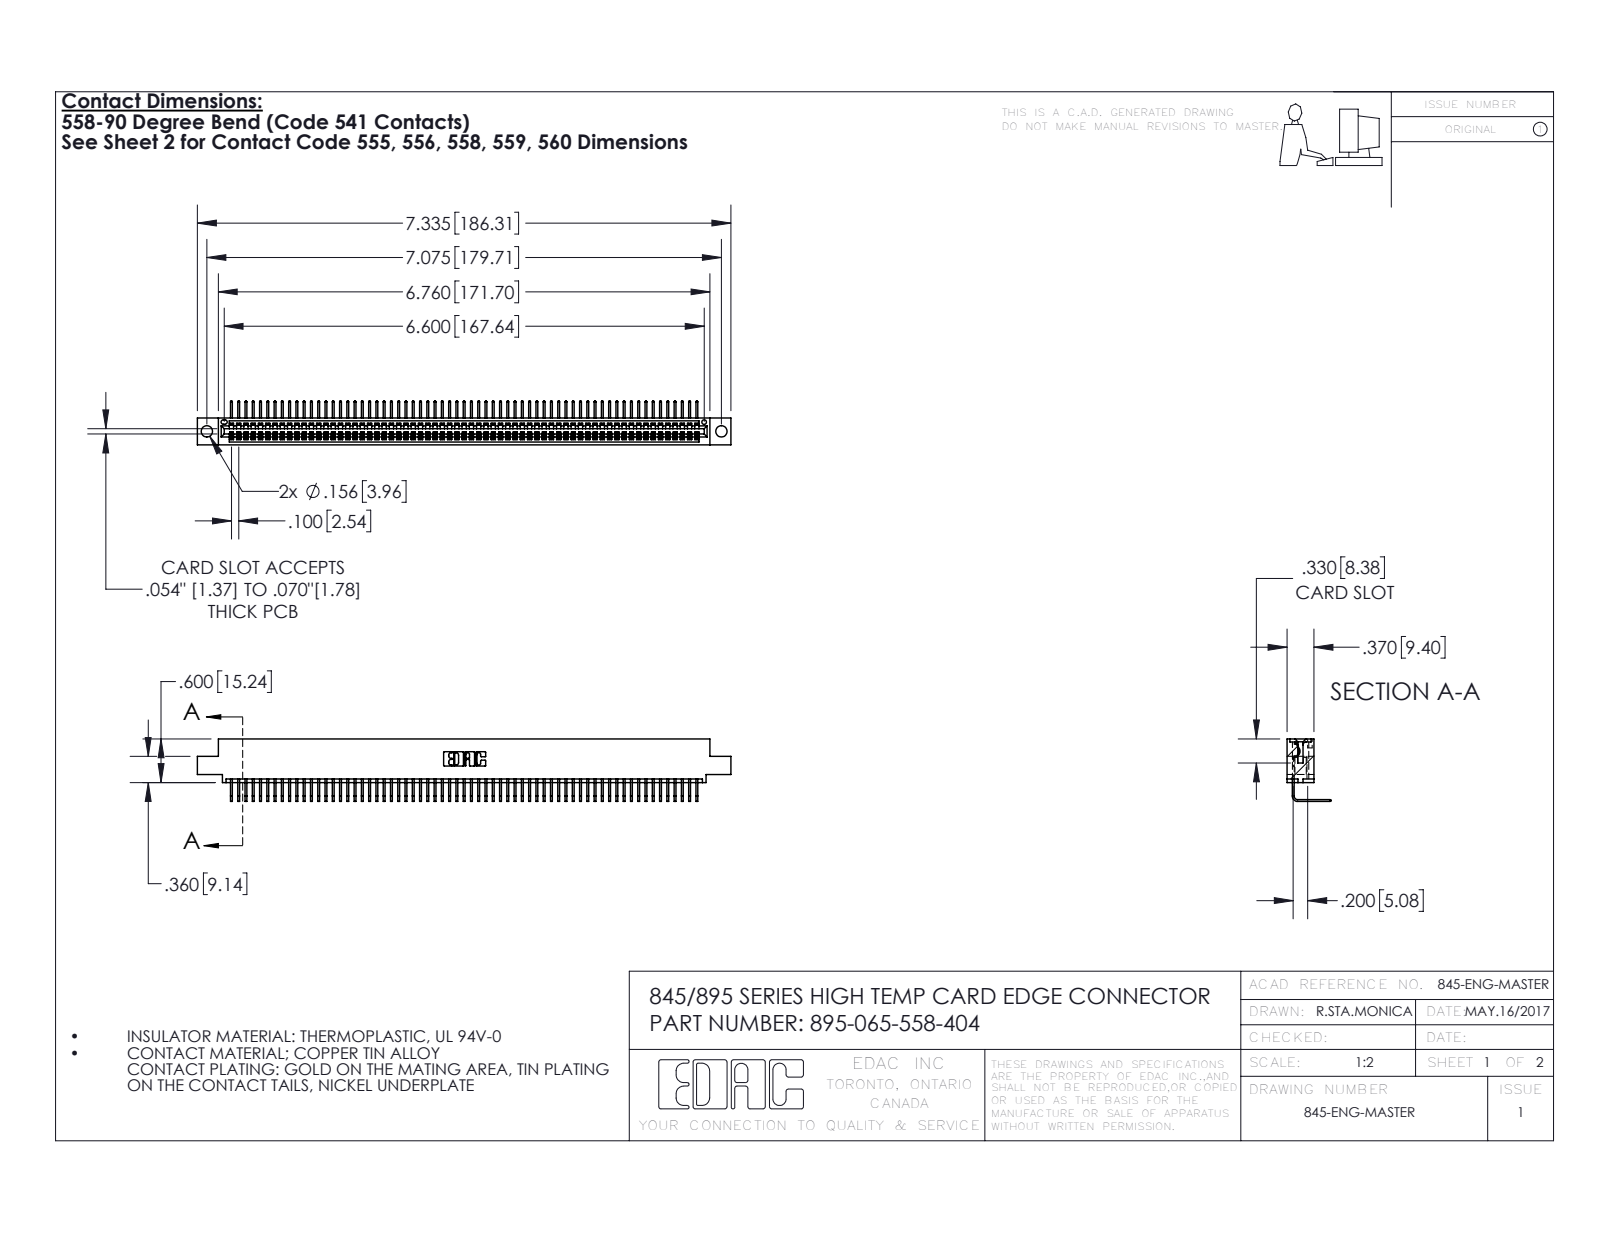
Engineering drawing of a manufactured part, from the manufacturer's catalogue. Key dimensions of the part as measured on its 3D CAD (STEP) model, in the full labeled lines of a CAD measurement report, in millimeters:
Part name (STEP PRODUCT): 345-292-001_558 Tail - 2; 345 Part_0.110 Offset - 0.156 Dia-TH; 395-065-558-404
STEP written by: SolidWorks 2016 (CONFIG_CONTROL_DESIGN)
Units: millimetres
Bodies: 66 solids, 4030 faces (2814 planar, 1216 cylindrical, 0 other)
Overall size (bounding box): 186.3 × 21.8 × 15.4
Volume: 17 940 mm³ · Surface area: 25 320 mm²
Round holes (diameter × count): ⌀4 ×2, ⌀1.6 ×1
Partial cylindrical surfaces — rounded edges, fillets, slot ends (radius × count): R0.2 ×130, R0.3 ×22, R0.2 ×6, R0.8 ×6, R0.7 ×3, R0.8 ×2, R1 ×2, R0.4 ×1
Main face-to-face distances: 1.8, 7.6, 9.4, 5.1, 2.5, 6.9, 0.6, 5.7, 3.8, 1.8
Hole centre spacings: 6.9, 173.7, 179.7
